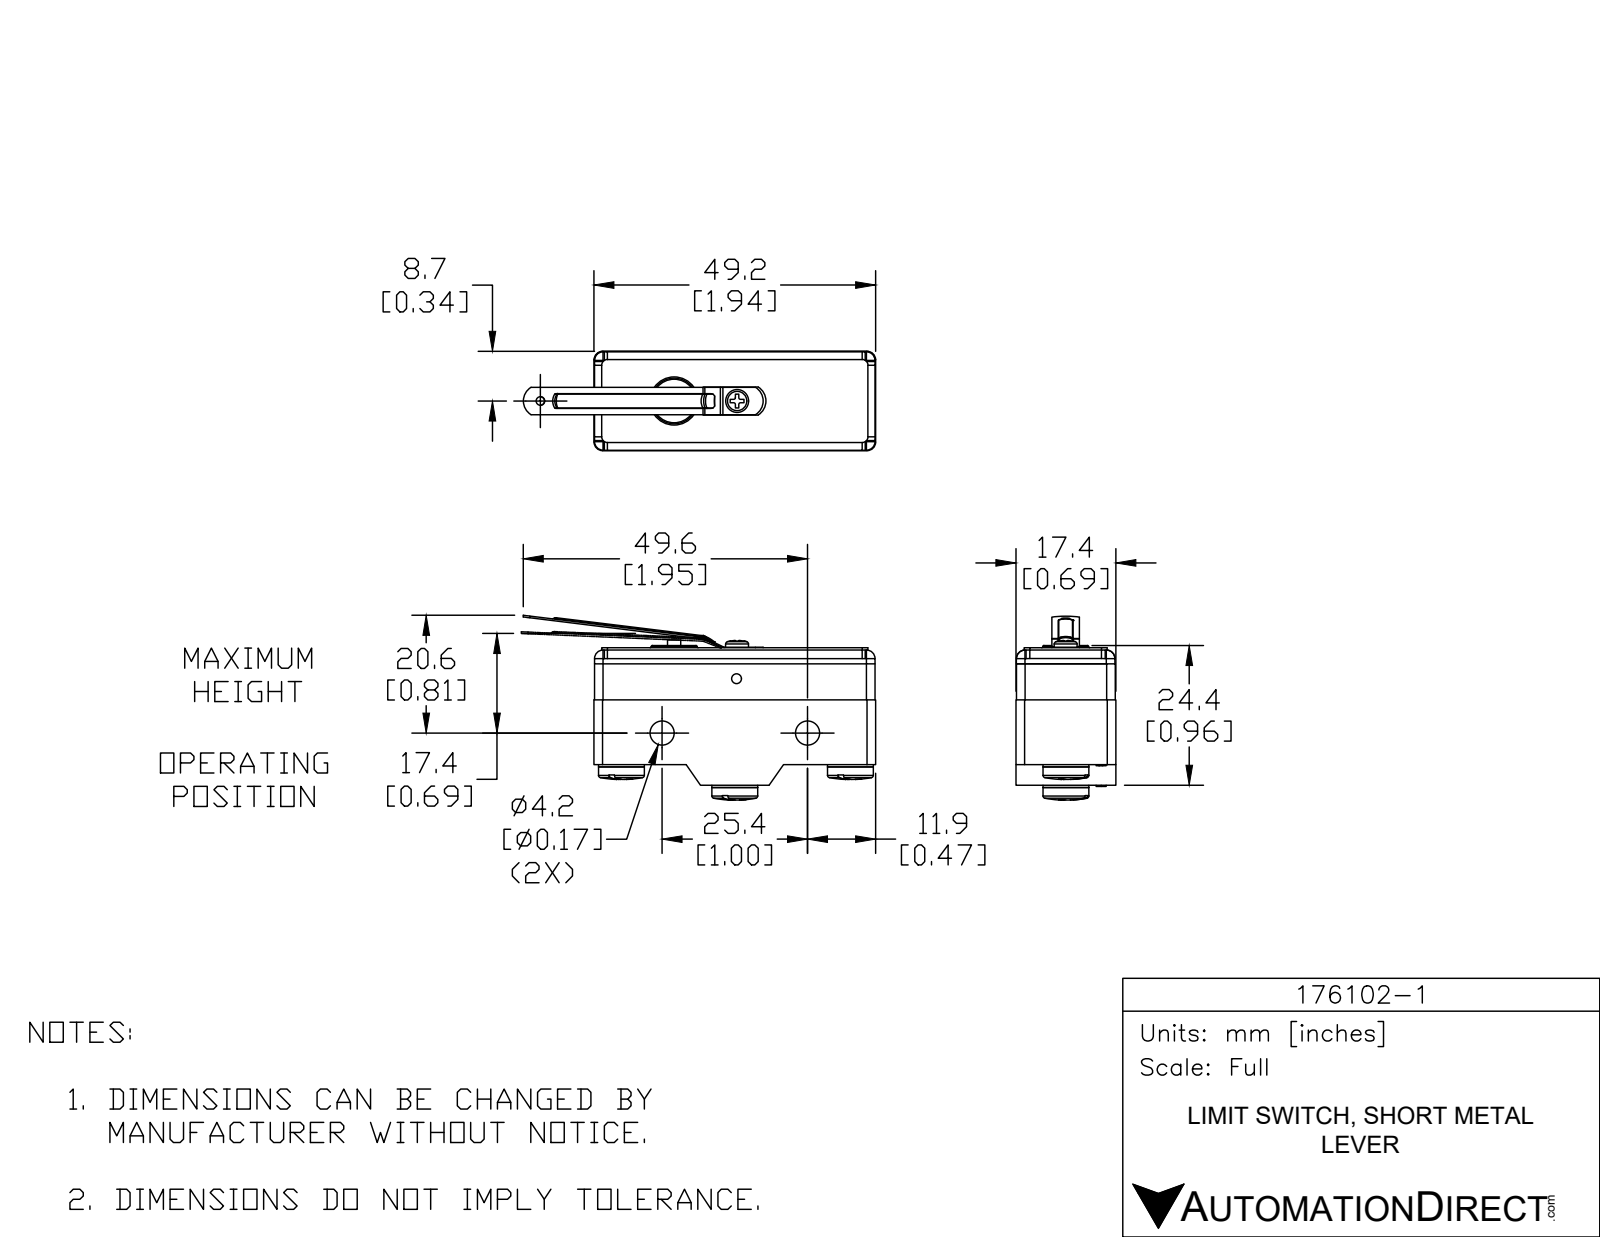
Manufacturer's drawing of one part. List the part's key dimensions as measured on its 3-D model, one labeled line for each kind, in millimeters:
Part name (STEP PRODUCT): 176-MS (Screw Terminal)-Short Lever
STEP written by: SolidWorks 2018 (AUTOMOTIVE_DESIGN)
Units: millimetres
Bodies: 11 solids, 555 faces (231 planar, 136 cylindrical, 188 other)
Overall size (bounding box): 61.4 × 31.9 × 17.4
Volume: 17 010 mm³ · Surface area: 8 645 mm²
Round holes (diameter × count): ⌀3.8 ×3, ⌀6 ×3, ⌀4.2 ×2, ⌀1.5 ×1, ⌀1.7 ×1, ⌀2.4 ×1, ⌀2.4 ×1, ⌀2.8 ×1
Round bosses / shafts (diameter × count): ⌀8 ×3, ⌀2.3 ×1
Partial cylindrical surfaces — rounded edges, fillets, slot ends (radius × count): R1.5 ×20, R0.3 ×16, R1 ×6, R0.1 ×4, R2.9 ×3, R2.8 ×2, R2.9 ×1
Main face-to-face distances: 20.4, 17.3, 2.8, 17.6, 17.4, 0.4, 3.6, 17.3, 24, 21.2
Hole centre spacings: 19.8, 20.2, 0.4, 9.2, 10.6, 11, 15.6, 16.1
